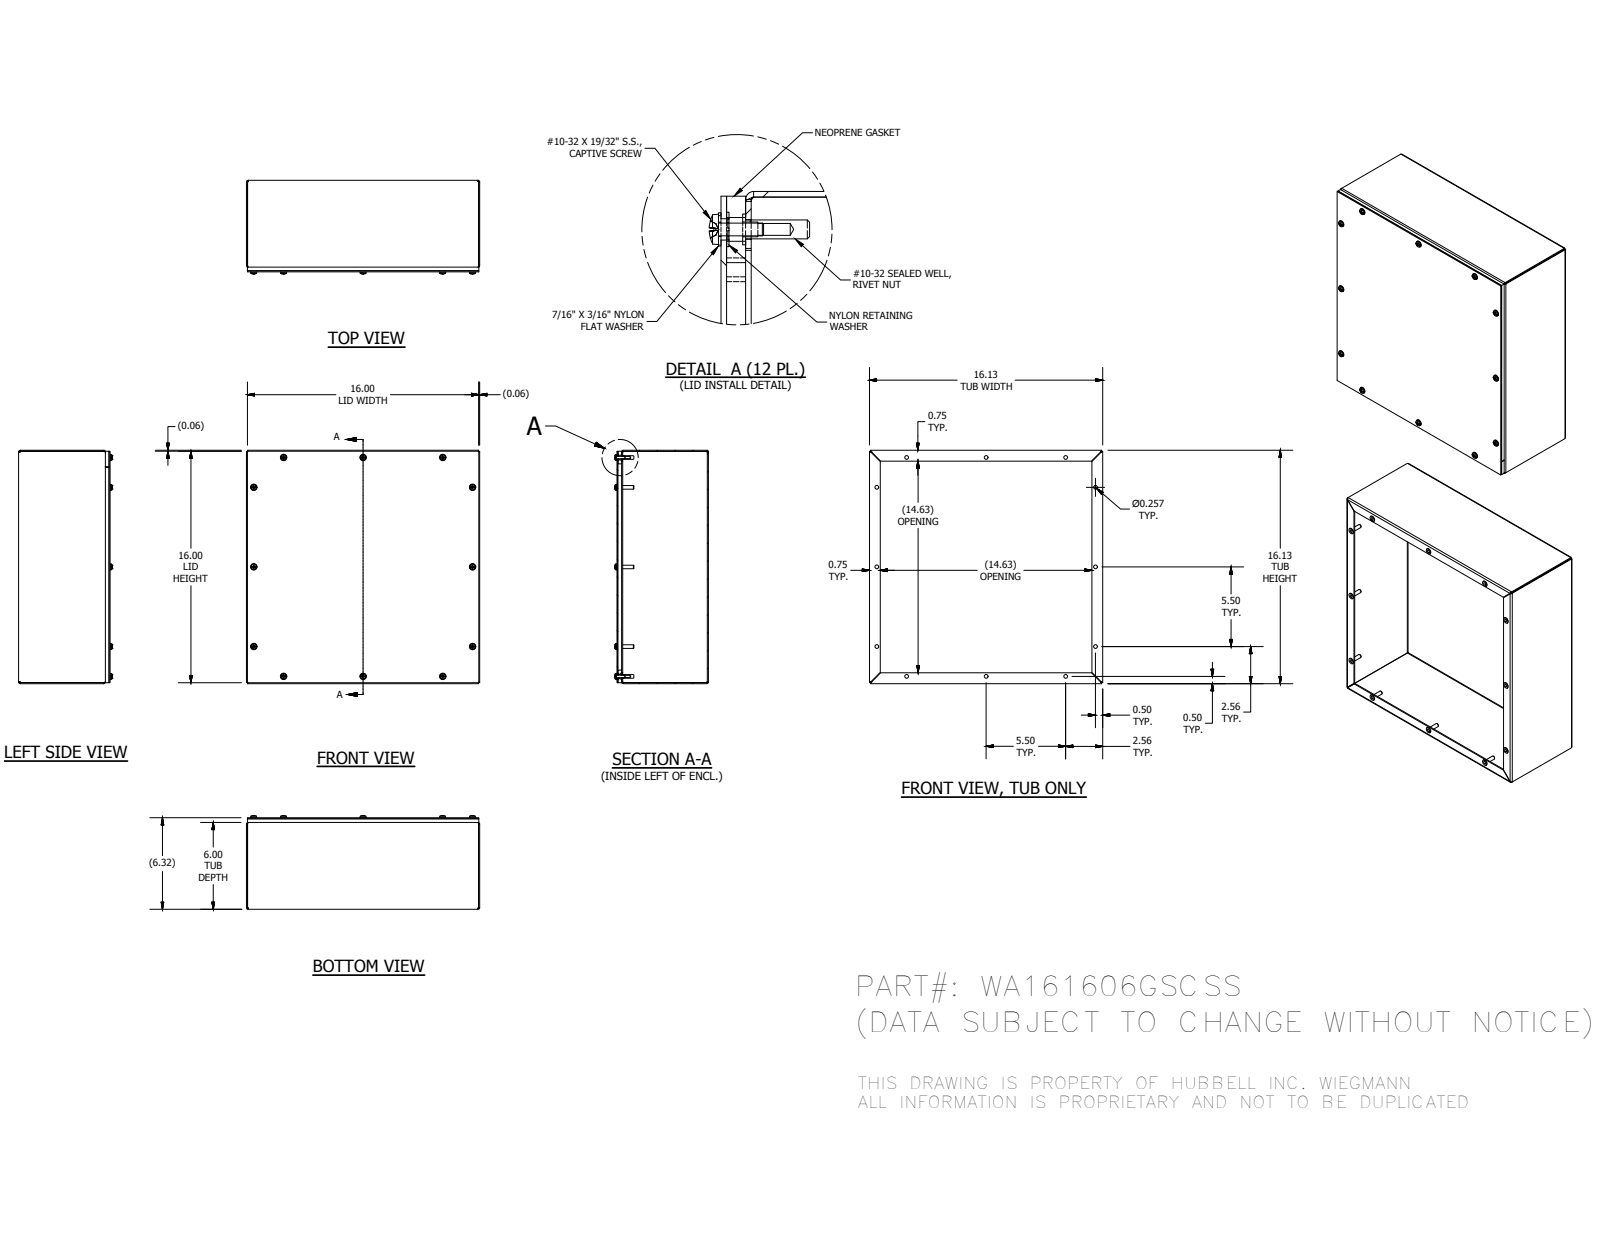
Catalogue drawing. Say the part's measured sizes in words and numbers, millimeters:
The part is named "WA161606GSCSSBKP; WA1616GSCSSLID; 37210; 39035 (+4 more)". Its 3-D file was written by "Autodesk Inventor 2016 (AUTOMOTIVE_DESIGN)". It is 52 solids with 1088 faces: 596 planar, 224 cylindrical and 268 other. Overall it measures 409.57 by 409.57 by 164.56 millimeters. Its volume is 1 354 000 cubic millimeters and its surface area 1 320 000 square millimeters. Round holes: 12 of diameter 3.96, 12 of diameter 4.78, 12 of diameter 4.98, 12 of diameter 6.53, 12 of diameter 7.06, 12 of diameter 7.14, 12 of diameter 7.95. Round bosses or shafts: 12 of diameter 11.51, 12 of diameter 11.11, 12 of diameter 10.31, 12 of diameter 6.3, 12 of diameter 4.25. Partial cylindrical surfaces (rounded edges, fillets, slot ends): 12 of radius 0.79, 12 of radius 2.27, 8 of radius 1.78, 8 of radius 2.67. The main face-to-face distances are 1.88, 158.75, 407.7, 160.63, 156.87, 405.82, 409.58, 150.52, 8.23, 6.35. The hole center spacings are 139.7, 279.4, 335.88, 335.9, 383.37, 408.77, 384.16, 74.08.
